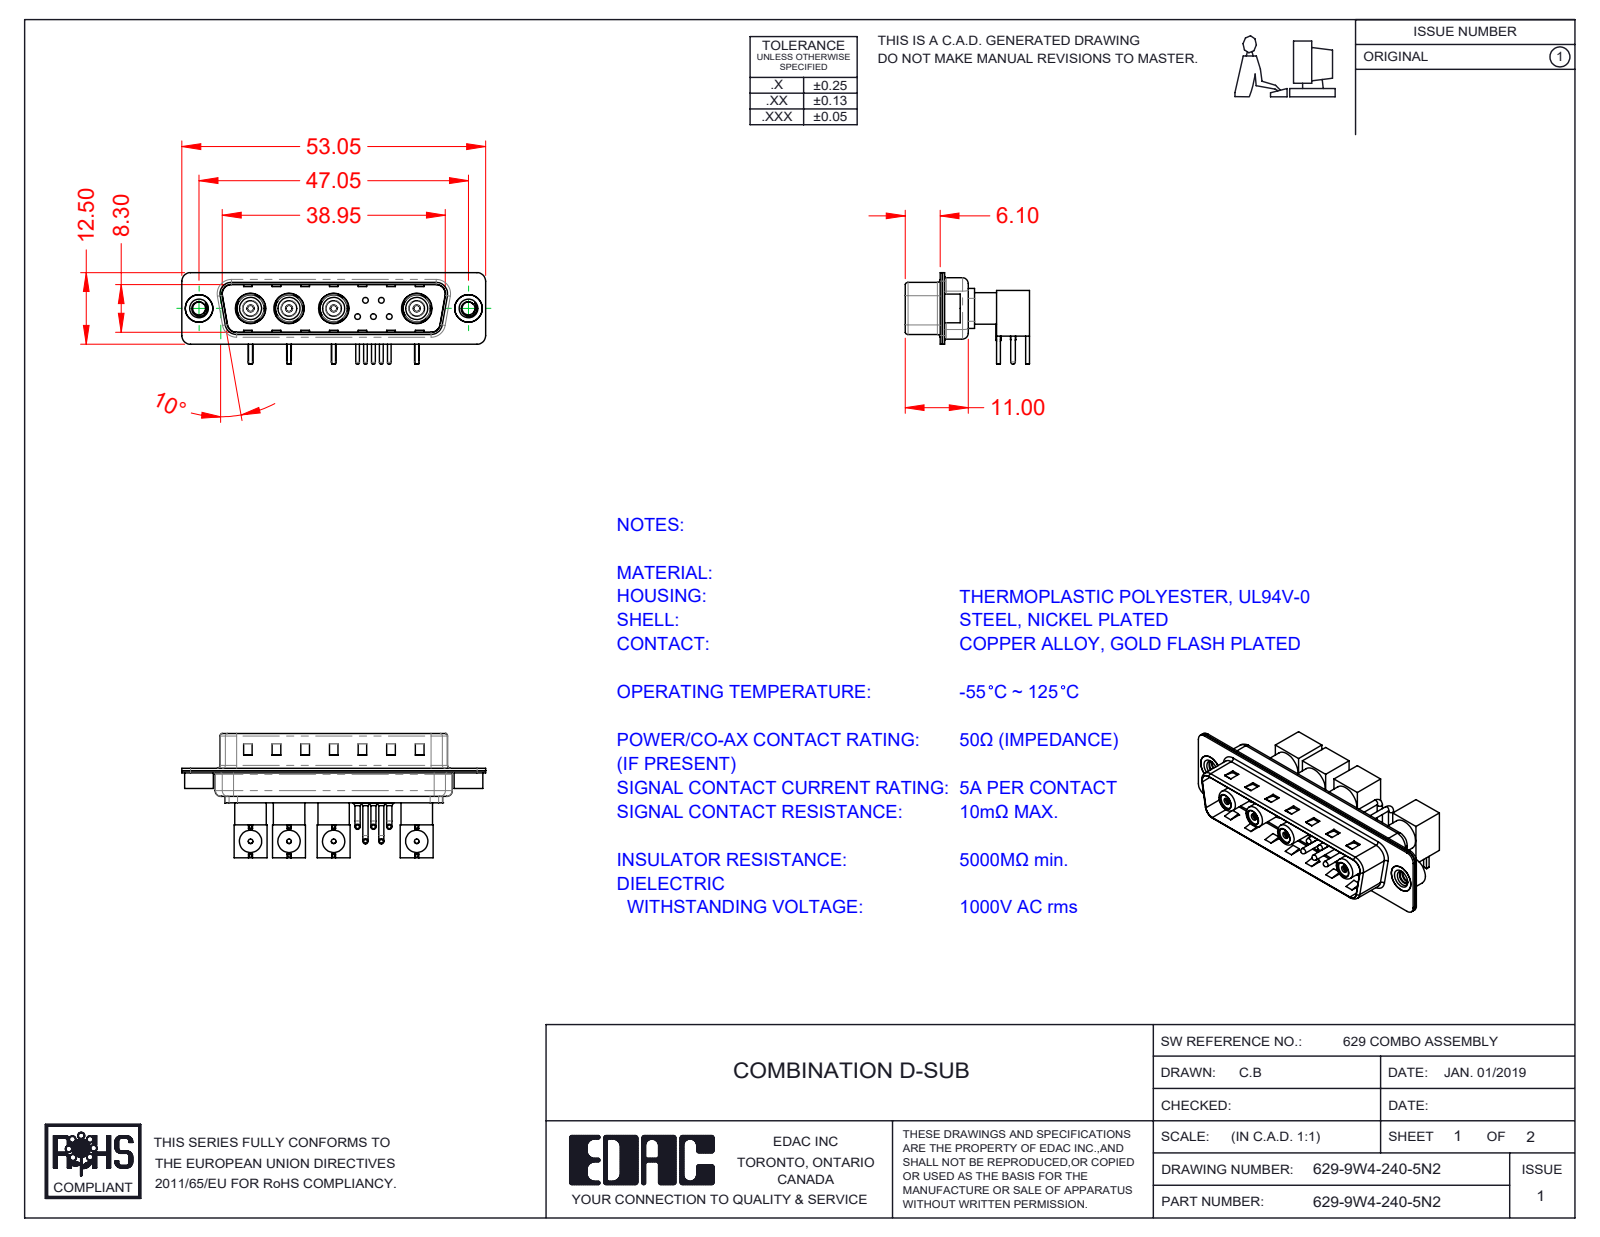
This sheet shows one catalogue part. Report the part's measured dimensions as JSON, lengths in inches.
{"part_name": "Co-Ax Jack Assy_RA; 629-9W4-240-5N2; 629Combo Contact Row 2; 629Combo Housing_9W4 (+8 more)", "step_written_by": "SolidWorks 2020 (CONFIG_CONTROL_DESIGN)", "units": "inches", "bodies": {"solids": 38, "faces": 1534, "planar": 719, "cylindrical": 585, "other": 230}, "overall_size": [2.089, 0.855, 0.63], "volume_in3": 0.238, "surface_area_in2": 16.47, "round_holes": [[0.063, 9], [0.03, 5], [0.079, 5], [0.031, 4], [0.043, 4], [0.047, 4], [0.059, 4], [0.098, 4], [0.106, 4], [0.122, 4], [0.134, 4], [0.154, 4]], "round_bosses_or_shafts": [[0.035, 10], [0.031, 8], [0.059, 5], [0.039, 5], [0.026, 5], [0.217, 4], [0.205, 4], [0.189, 4]], "partial_cylinders_radius": [[0.059, 16], [0.079, 12], [0.02, 8], [0.063, 8], [0.04, 5], [0.01, 4], [0.024, 4], [0.026, 4]], "face_to_face_distances": [0.016, 0.031, 0.374, 0.226, 0.358, 0.343, 0.39, 0.014, 0.055, 0.018], "hole_center_spacings": [0.571, 0.265, 0.572, 0.124, 0.307, 0.307, 0.571, 0.878]}
